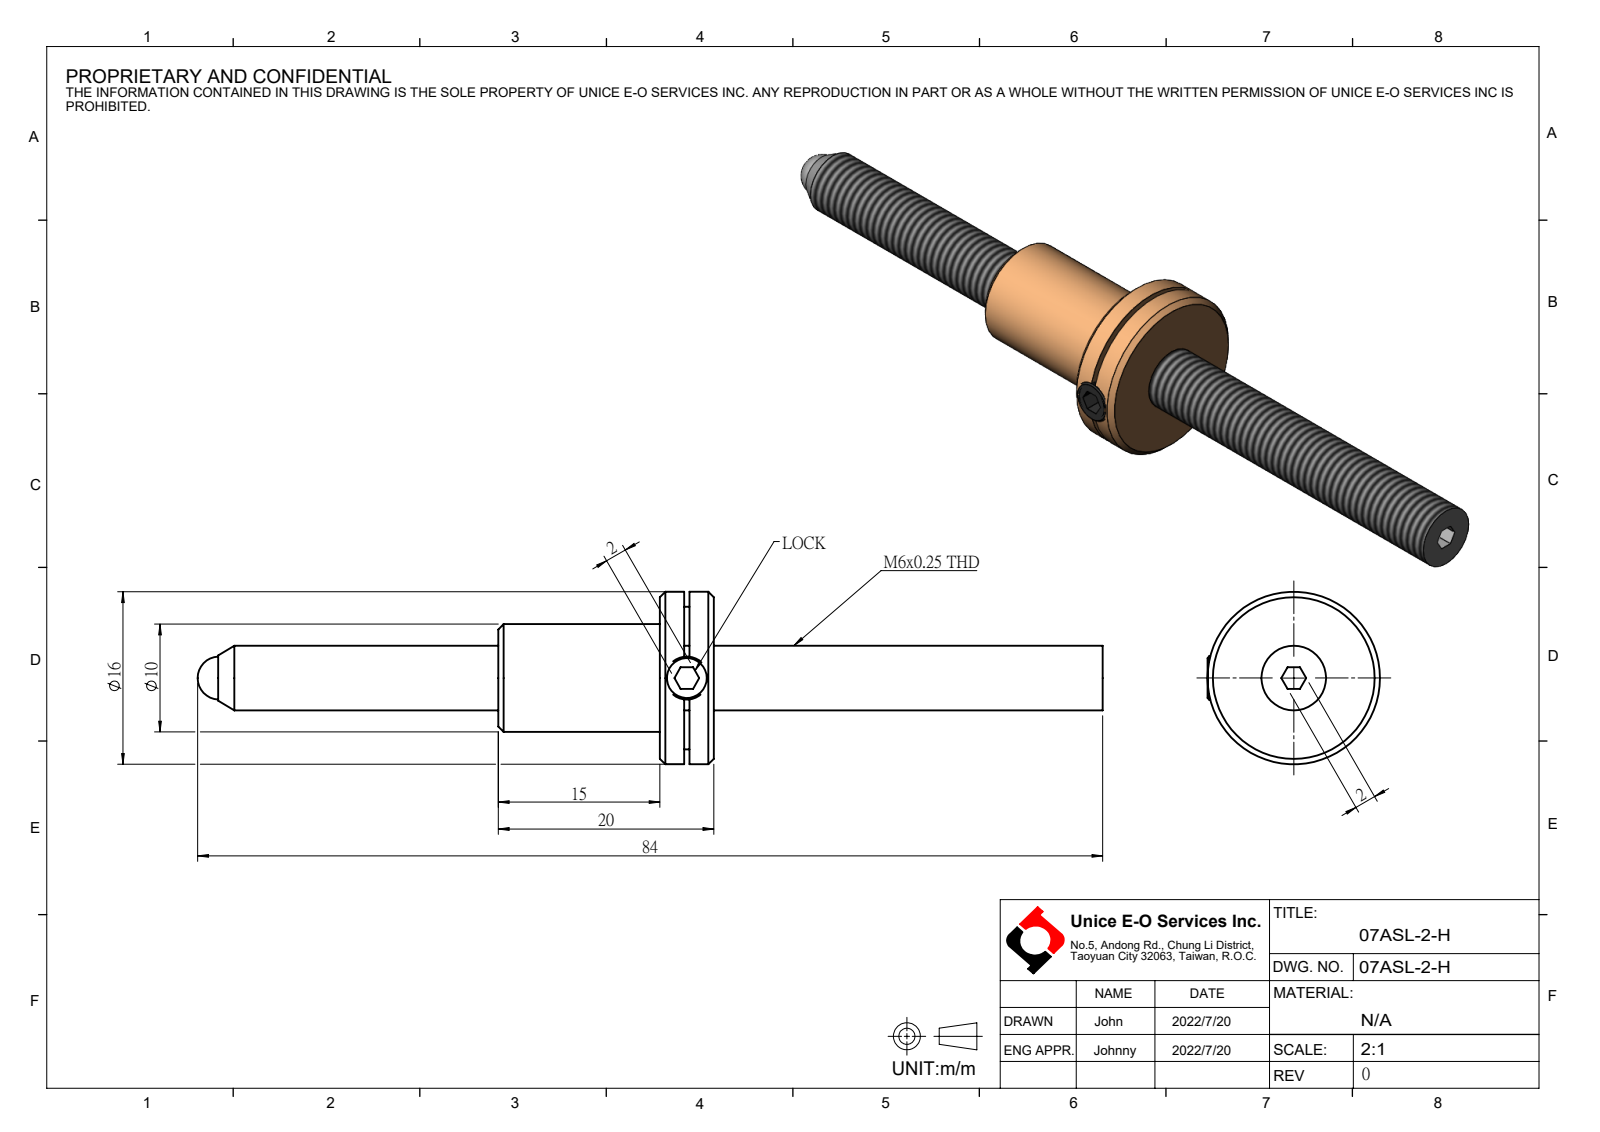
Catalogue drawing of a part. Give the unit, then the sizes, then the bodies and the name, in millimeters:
Units: millimetres
Overall size (bounding box): 84 × 16.2 × 16
Round holes (diameter × count): ⌀3.3 ×1, ⌀4 ×1, ⌀5 ×1
Round bosses / shafts (diameter × count): ⌀16 ×1, ⌀10 ×1, ⌀6 ×1, ⌀4 ×1
Main face-to-face distances: 2.25, 2.75, 0.5, 5, 15, 17.25, 17.75, 20, 56.1, 41.1
Volume: 4 020 mm³ · Surface area: 3 404 mm²
Bodies: 4 solids, 67 faces (23 planar, 17 cylindrical, 27 other)
Part name (STEP PRODUCT): 07ASL-2-H
STEP written by: SolidWorks 2021 (CONFIG_CONTROL_DESIGN)
